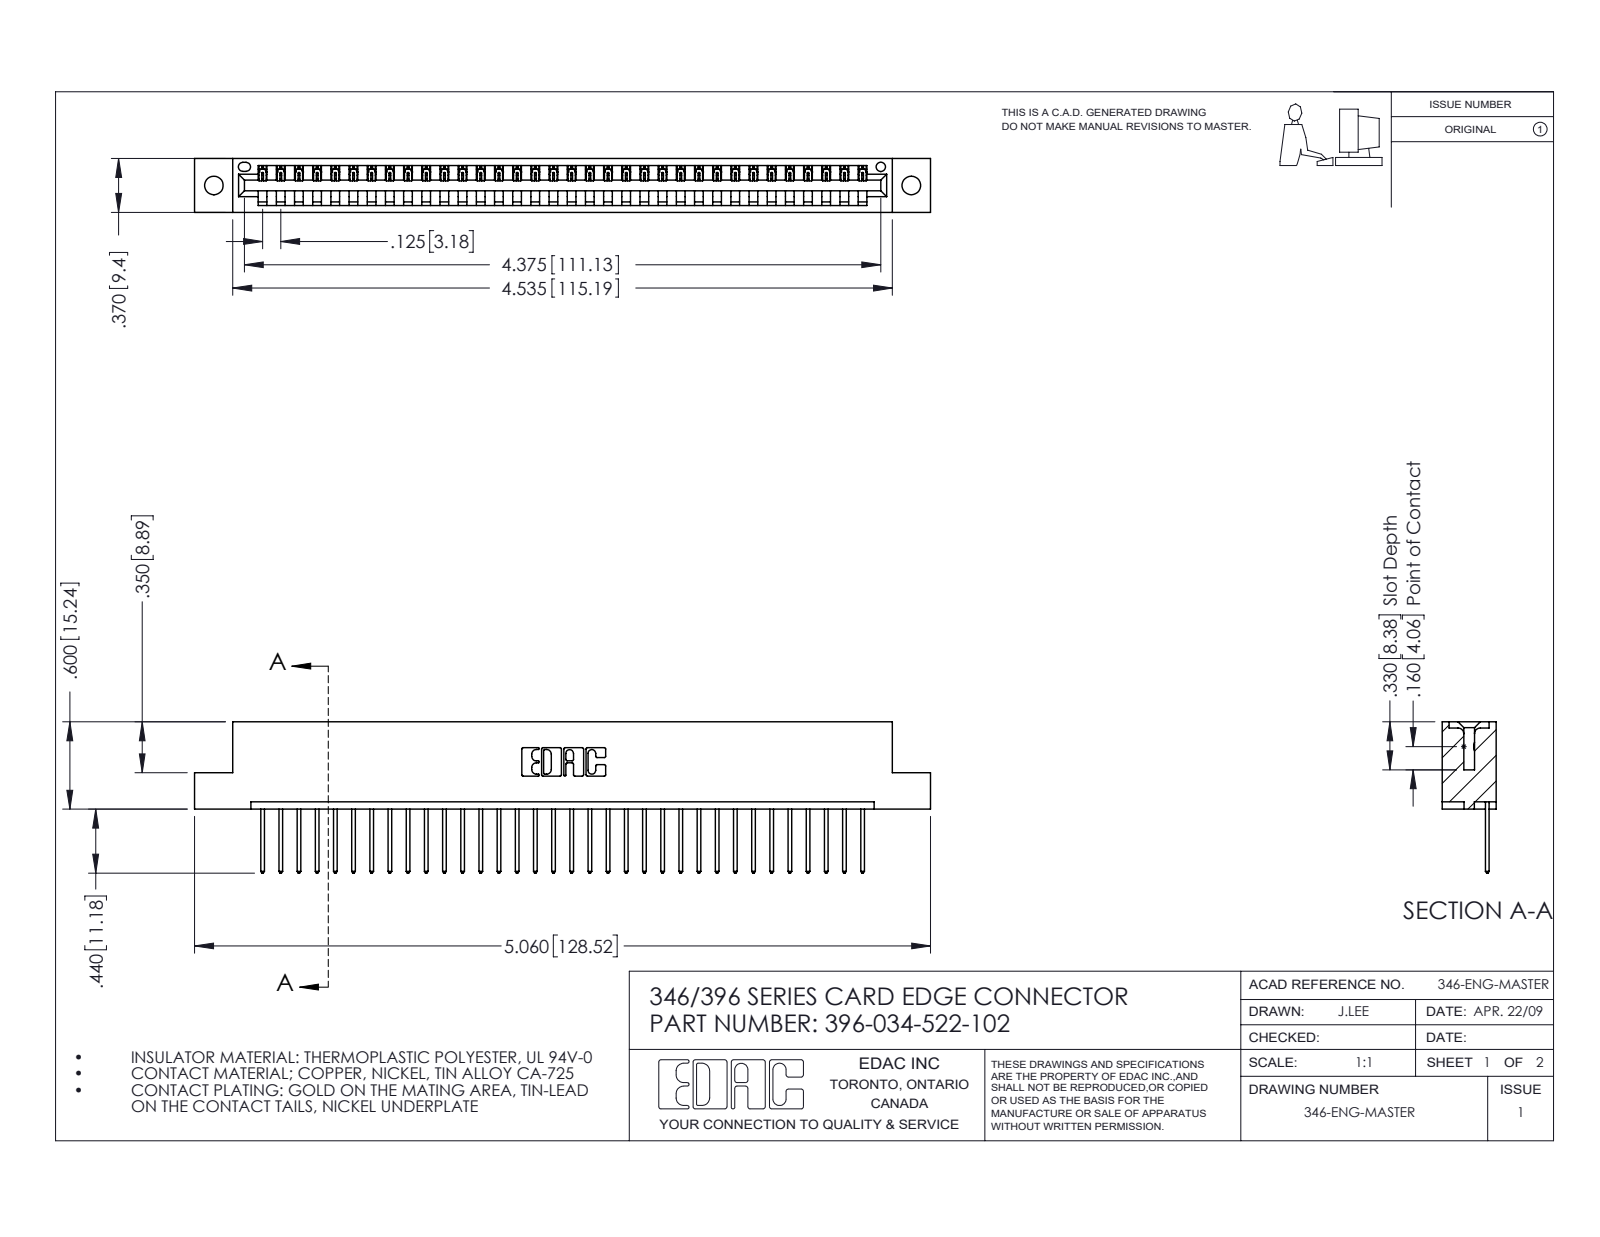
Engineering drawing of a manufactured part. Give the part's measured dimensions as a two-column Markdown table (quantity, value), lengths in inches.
| quantity | value |
| --- | --- |
| part name | 345-292-001_345-293-122; 346 Part_Flush Mounting Lugs - 0.128 Dia; 396-034-522-102 |
| STEP written by | SolidWorks 2016 (CONFIG_CONTROL_DESIGN) |
| units | inches |
| bodies | 35 solids, 2094 faces (1436 planar, 658 cylindrical, 0 other) |
| overall size | 5.06 × 1.04 × 0.37 |
| volume | 0.745 in³ |
| surface area | 23.3 in² |
| round holes (diameter × count) | 0.128 × 2, 0.064 × 1 |
| partial cylindrical surfaces (radius × count) | 0.006 × 68, 0.01 × 68, 0.01 × 22, 0.007 × 6, 0.031 × 6, 0.026 × 3, 0.031 × 2, 0.04 × 2 |
| main face-to-face distances | 0.048, 0.322, 0.37, 0.25, 0.072, 0.298, 0.025, 0.148, 0.222, 0.1 |
| hole center spacings | 0.246, 4.587, 4.795 |
